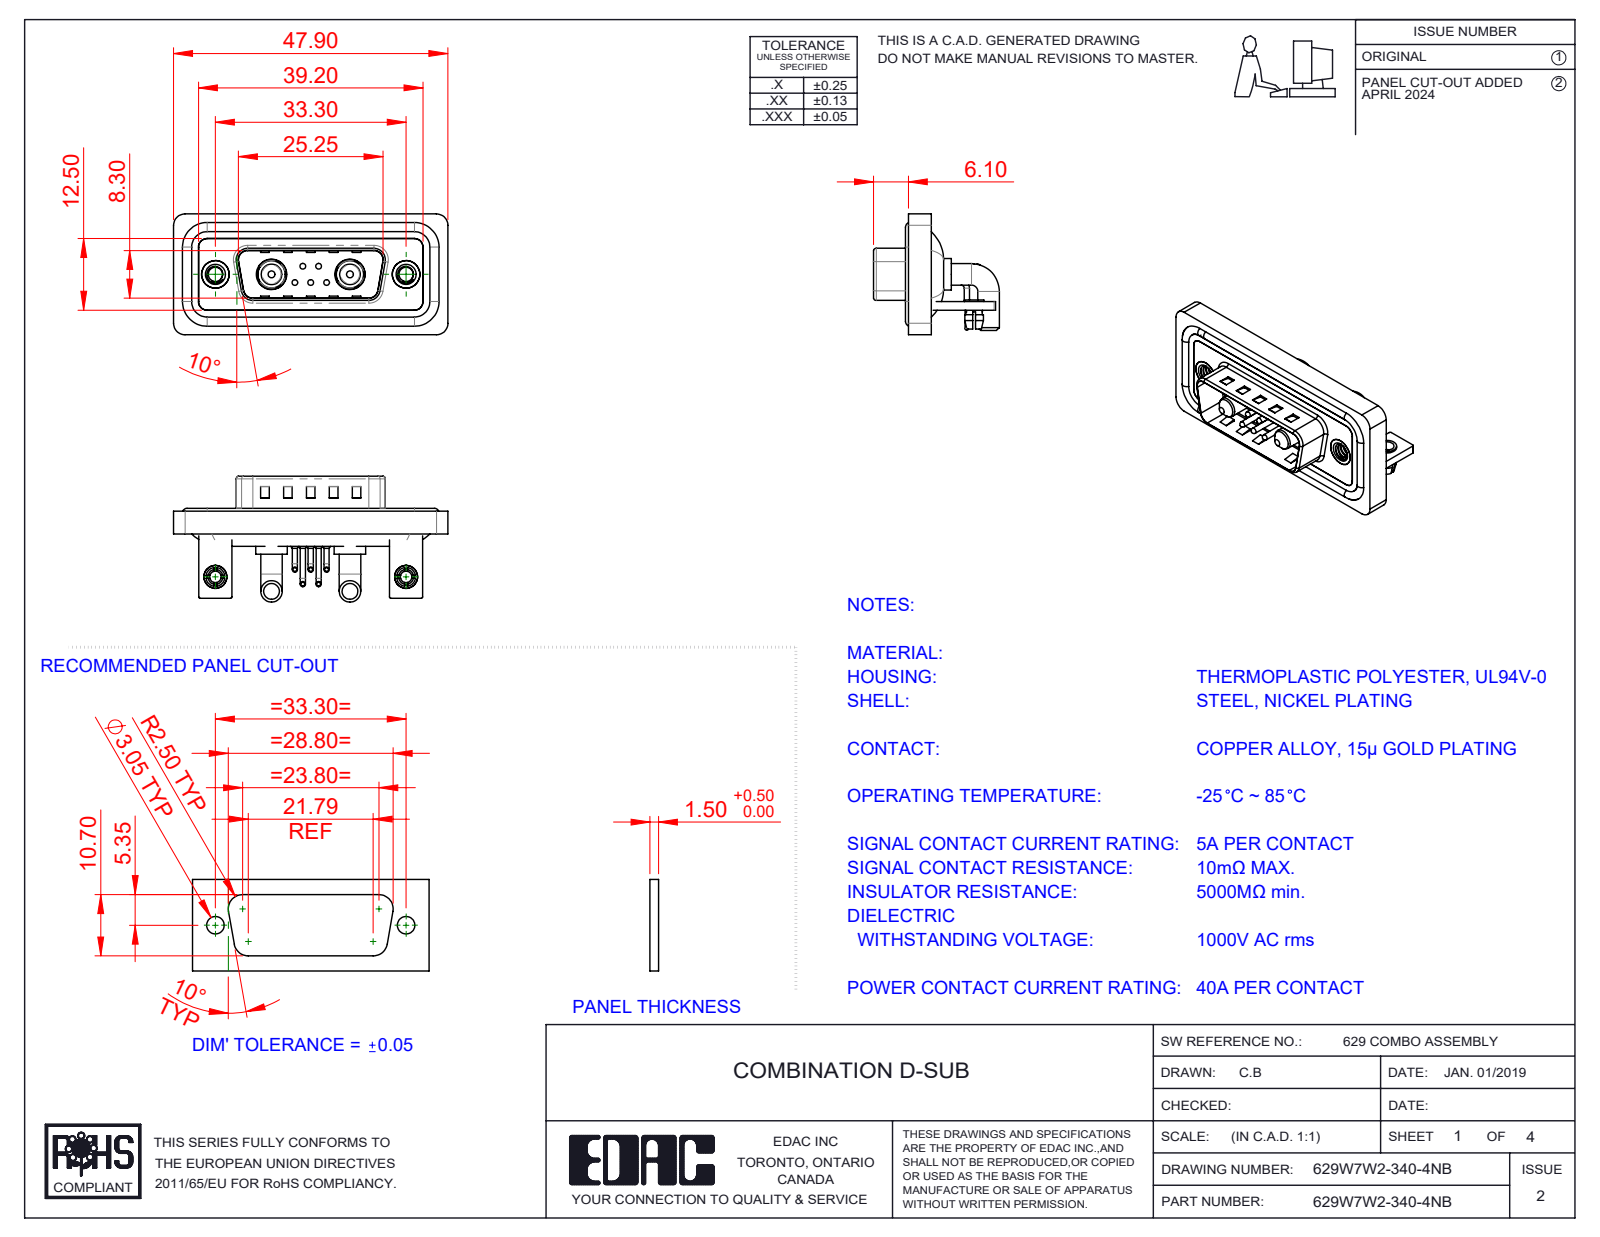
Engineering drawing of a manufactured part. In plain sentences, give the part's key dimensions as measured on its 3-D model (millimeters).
The part is named "629Combo Shell Front_15 Contacts; 629Combo Waterproof Housing_15 Contacts; 629Combo Contact Row 1; 629Combo Board Lock (+7 more)". Its 3-D file was written by "SolidWorks 2023 (CONFIG_CONTROL_DESIGN)". It is 20 solids with 1213 faces: 585 planar, 456 cylindrical and 172 other. Overall it measures 47.9 by 21.98 by 21.1 millimeters. Its volume is 6 135 cubic millimeters and its surface area 10 027 square millimeters. Round holes: 7 of diameter 2, 5 of diameter 0.75, 5 of diameter 1.6, 4 of diameter 2.5, 2 of diameter 3.2, 2 of diameter 4, 2 of diameter 4.8, 2 of diameter 4.85, 2 of diameter 5, 2 of diameter 5.3. Round bosses or shafts: 10 of diameter 0.9, 5 of diameter 1.5, 5 of diameter 1, 5 of diameter 0.65, 4 of diameter 3.75, 4 of diameter 1.6, 2 of diameter 5.5, 2 of diameter 5.2. Partial cylindrical surfaces (rounded edges, fillets, slot ends): 21 of radius 2, 18 of radius 1.5, 16 of radius 0.25, 9 of radius 0.5, 8 of radius 1.6, 5 of radius 1.01, 4 of radius 0.6, 4 of radius 0.65. The main face-to-face distances are 0.4, 1.5, 0.8, 2.9, 2.1, 1.1, 1.6, 1.2, 3.7, 4.5. The hole center spacings are 3.16, 2.77, 9.8, 23.5, 33.3, 4.31, 4.33, 5.03.
